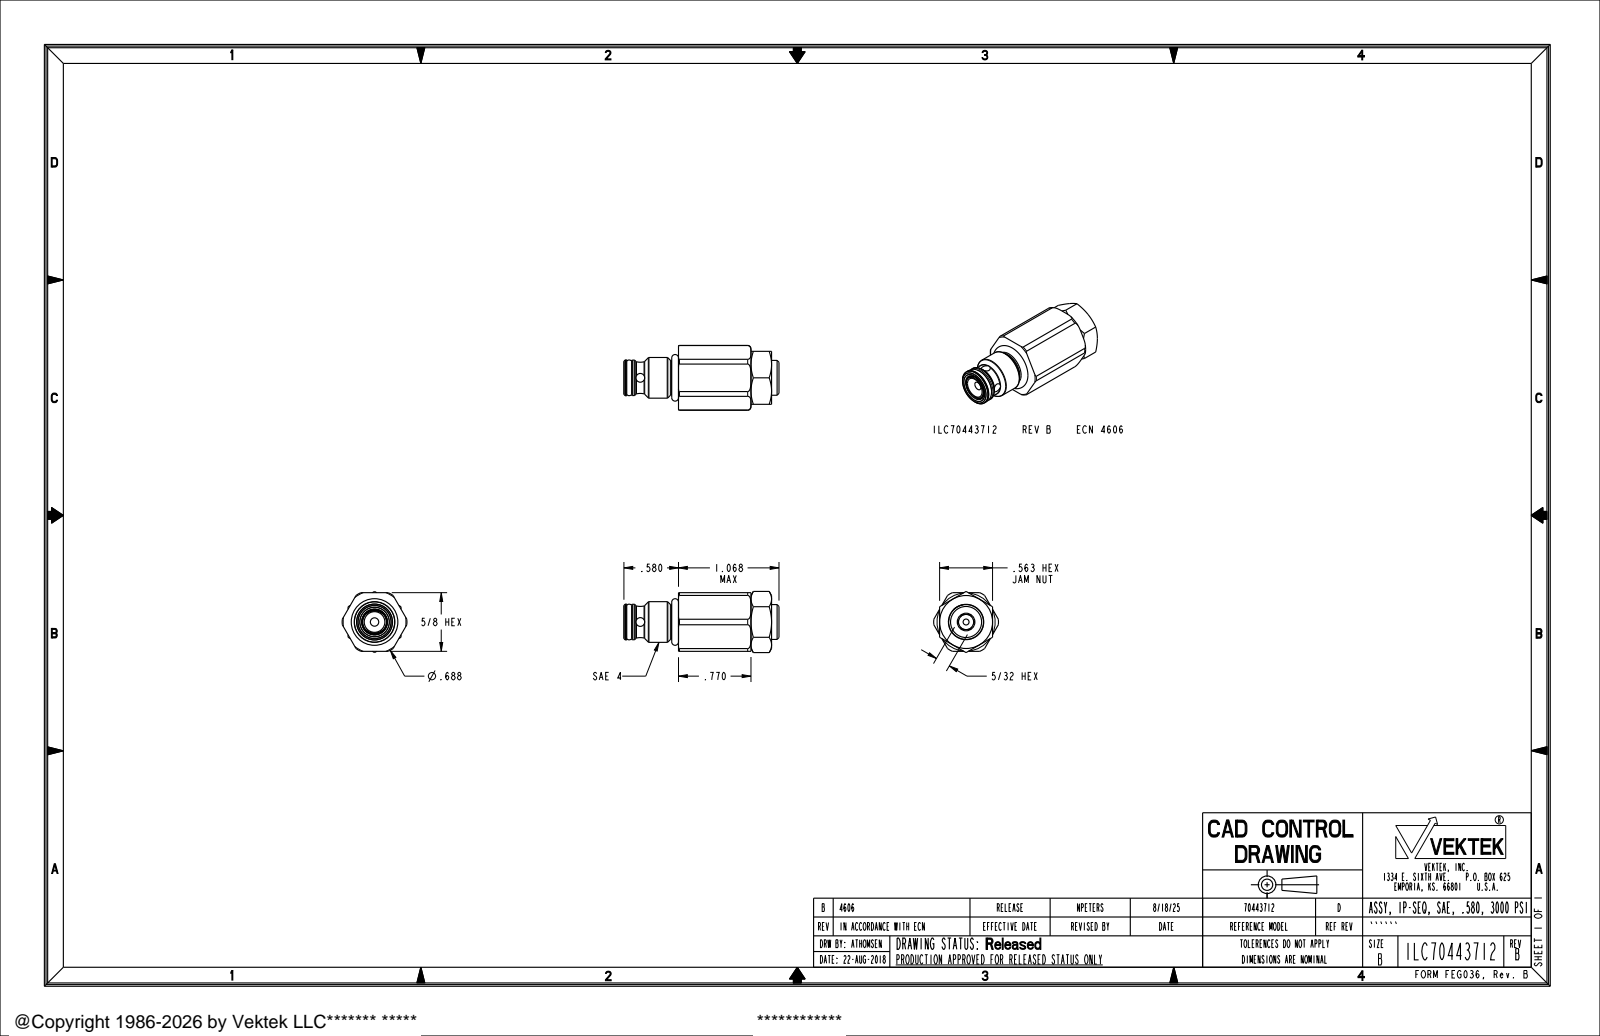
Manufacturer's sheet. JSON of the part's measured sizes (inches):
{"part_name": "ILC70443712", "step_written_by": "CREO PARAMETRIC BY PTC INC, 2021164 (AUTOMOTIVE_DESIGN)", "units": "inches", "bodies": {"solids": 1, "faces": 214, "planar": 45, "cylindrical": 69, "other": 100}, "overall_size": [1.648, 0.688, 0.65], "volume_in3": 0.386, "surface_area_in2": 4.536, "round_holes": [[0.093, 2], [0.161, 1], [0.247, 1], [0.27, 1], [0.375, 1], [0.5, 1], [0.528, 1]], "round_bosses_or_shafts": [[0.432, 1], [0.382, 1], [0.377, 1], [0.37, 1], [0.364, 1], [0.344, 1], [0.236, 1]], "partial_cylinders_radius": [[0.115, 2], [0.094, 1], [0.344, 1]], "face_to_face_distances": [0.623, 0.562, 0.77, 0.219, 0.989, 0.052, 0.27, 0.718, 0.079, 0.298]}
